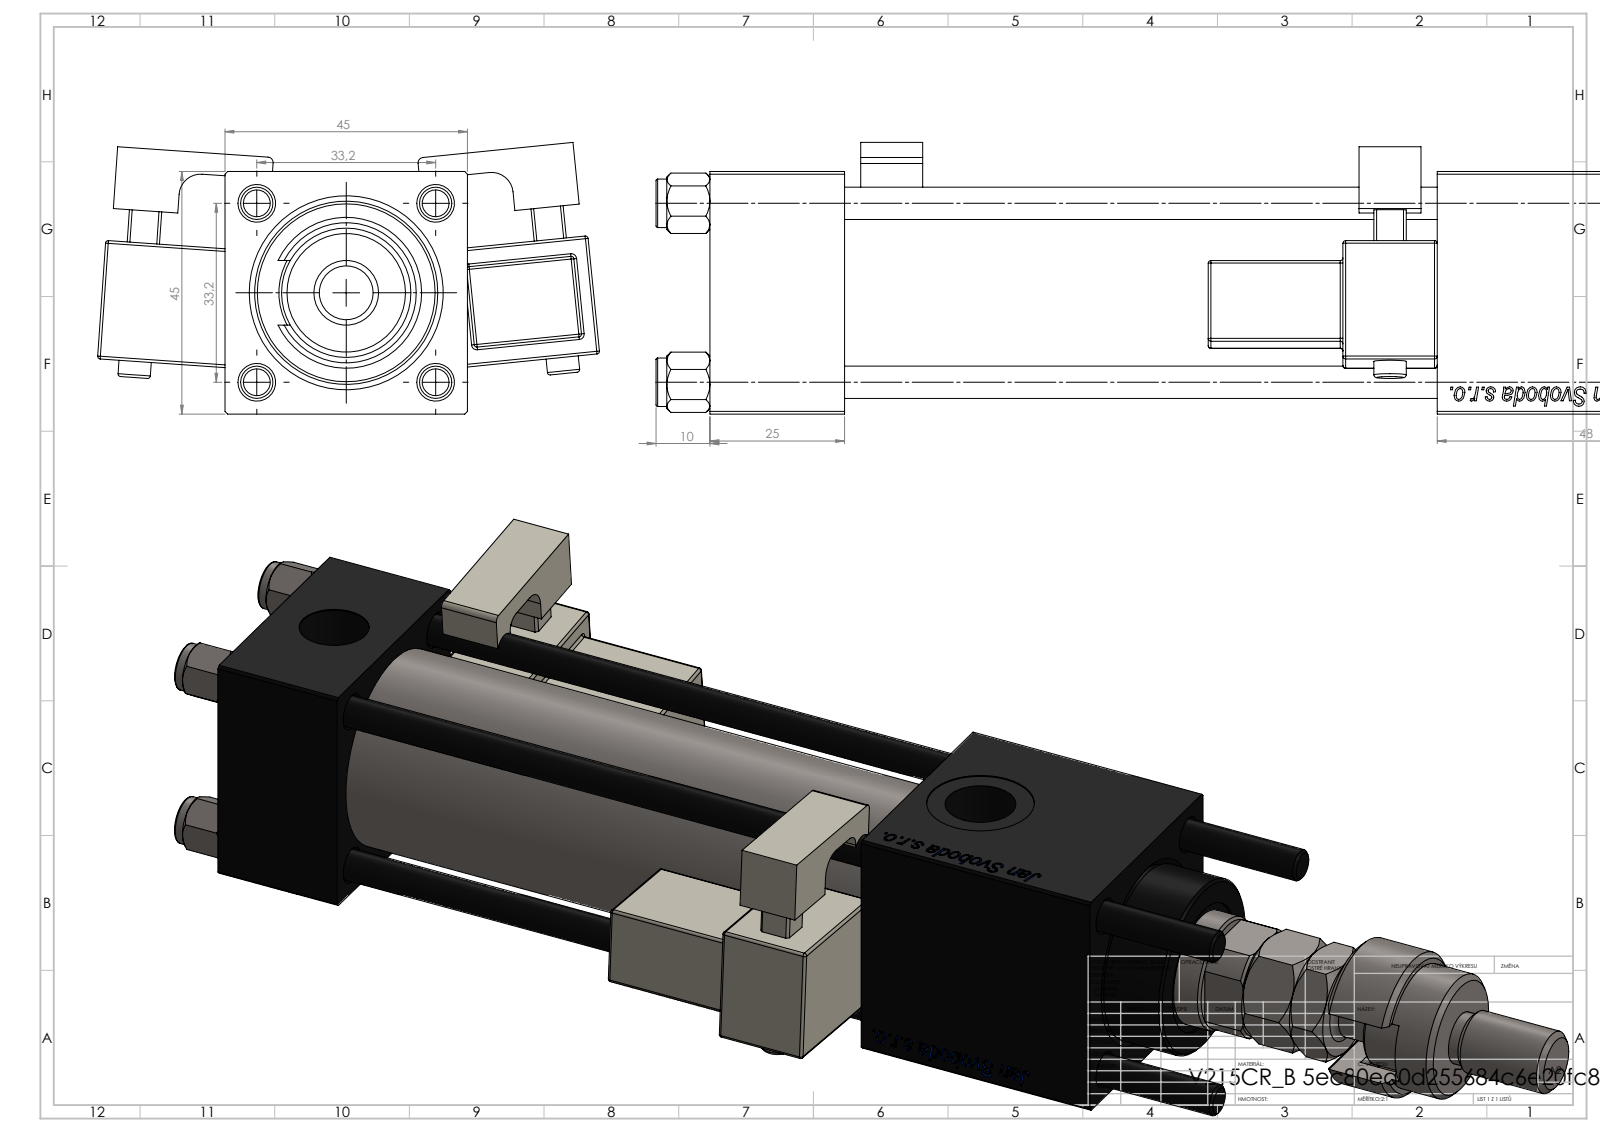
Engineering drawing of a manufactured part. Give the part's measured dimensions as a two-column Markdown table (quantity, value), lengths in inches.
| quantity | value |
| --- | --- |
| part name | V215_VC_A; V215CR_MSU; V215CR_VCP_B; V215CR_B_TYCINKA (+4 more) |
| STEP written by | SolidWorks 2019 (CONFIG_CONTROL_DESIGN) |
| units | inches |
| bodies | 15 solids, 1399 faces (519 planar, 152 cylindrical, 728 other) |
| overall size | 10.984 × 3.667 × 1.984 |
| volume | 19.66 in³ |
| surface area | 182.5 in² |
| round holes (diameter × count) | 0.236 × 4, 0.276 × 2, 0.518 × 2, 0.413 × 1, 0.512 × 1, 0.787 × 1, 0.866 × 1, 0.945 × 1, 0.984 × 1, 1.26 × 1, 1.299 × 1 |
| round bosses / shafts (diameter × count) | 0.354 × 4, 0.236 × 2, 1.496 × 1, 1.339 × 1, 1.102 × 1, 0.709 × 1, 0.472 × 1, 0.433 × 1 |
| partial cylindrical surfaces (radius × count) | 0.02 × 48, 0.039 × 2, 0.098 × 2, 0.157 × 2, 0.384 × 1, 0.413 × 1 |
| main face-to-face distances | 1.772, 0.984, 5.315, 4.331, 0.118, 7.205, 0.571, 0.591, 3.642, 0.689 |
| hole center spacings | 0.924, 1.307, 1.848, 5.341 |
